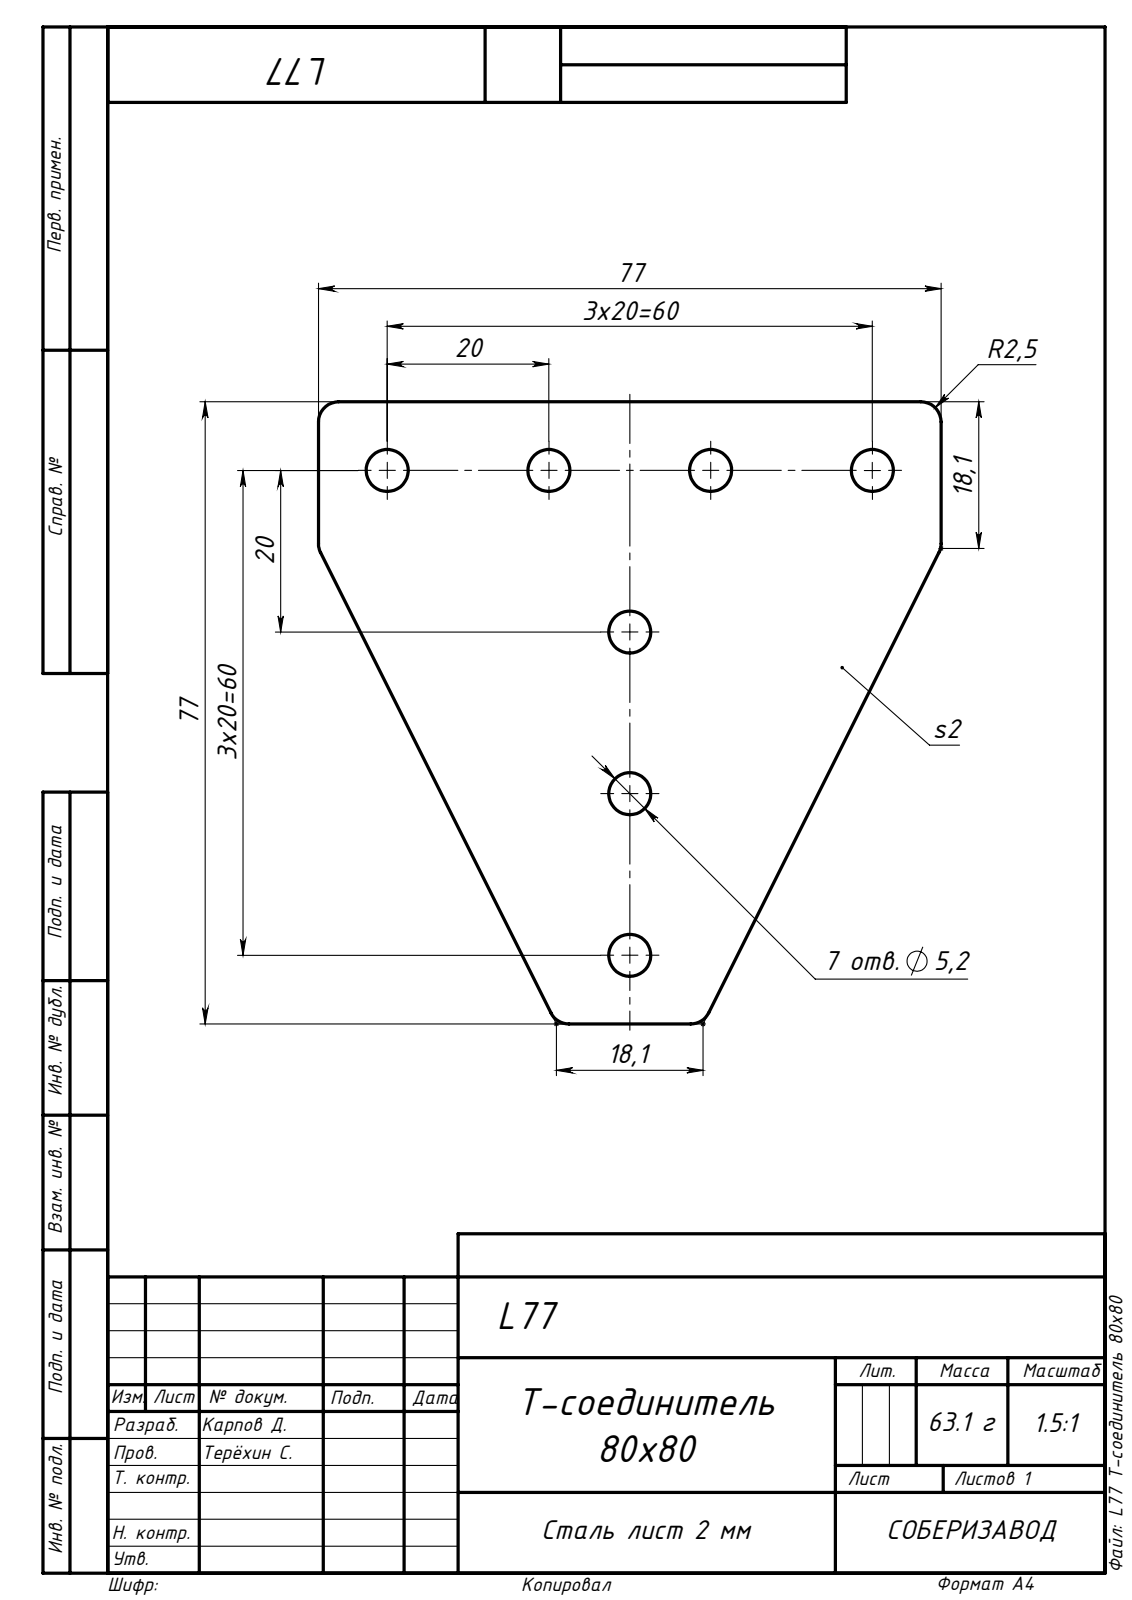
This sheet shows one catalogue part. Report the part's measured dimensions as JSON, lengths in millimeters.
{"part_name": "L77 Т-соединитель 80х80", "step_written_by": "SolidWorks 2019 (AUTOMOTIVE_DESIGN)", "units": "millimeters", "bodies": {"solids": 1, "faces": 28, "planar": 8, "cylindrical": 20, "other": 0}, "overall_size": [77, 77, 2], "volume_mm3": 8090, "surface_area_mm2": 8839, "round_holes": [[5.2, 7]], "partial_cylinders_radius": [[2.5, 6]], "face_to_face_distances": [2, 77], "hole_center_spacings": [20, 40, 22.36, 36.06, 41.23, 50, 60.83, 67.08]}
